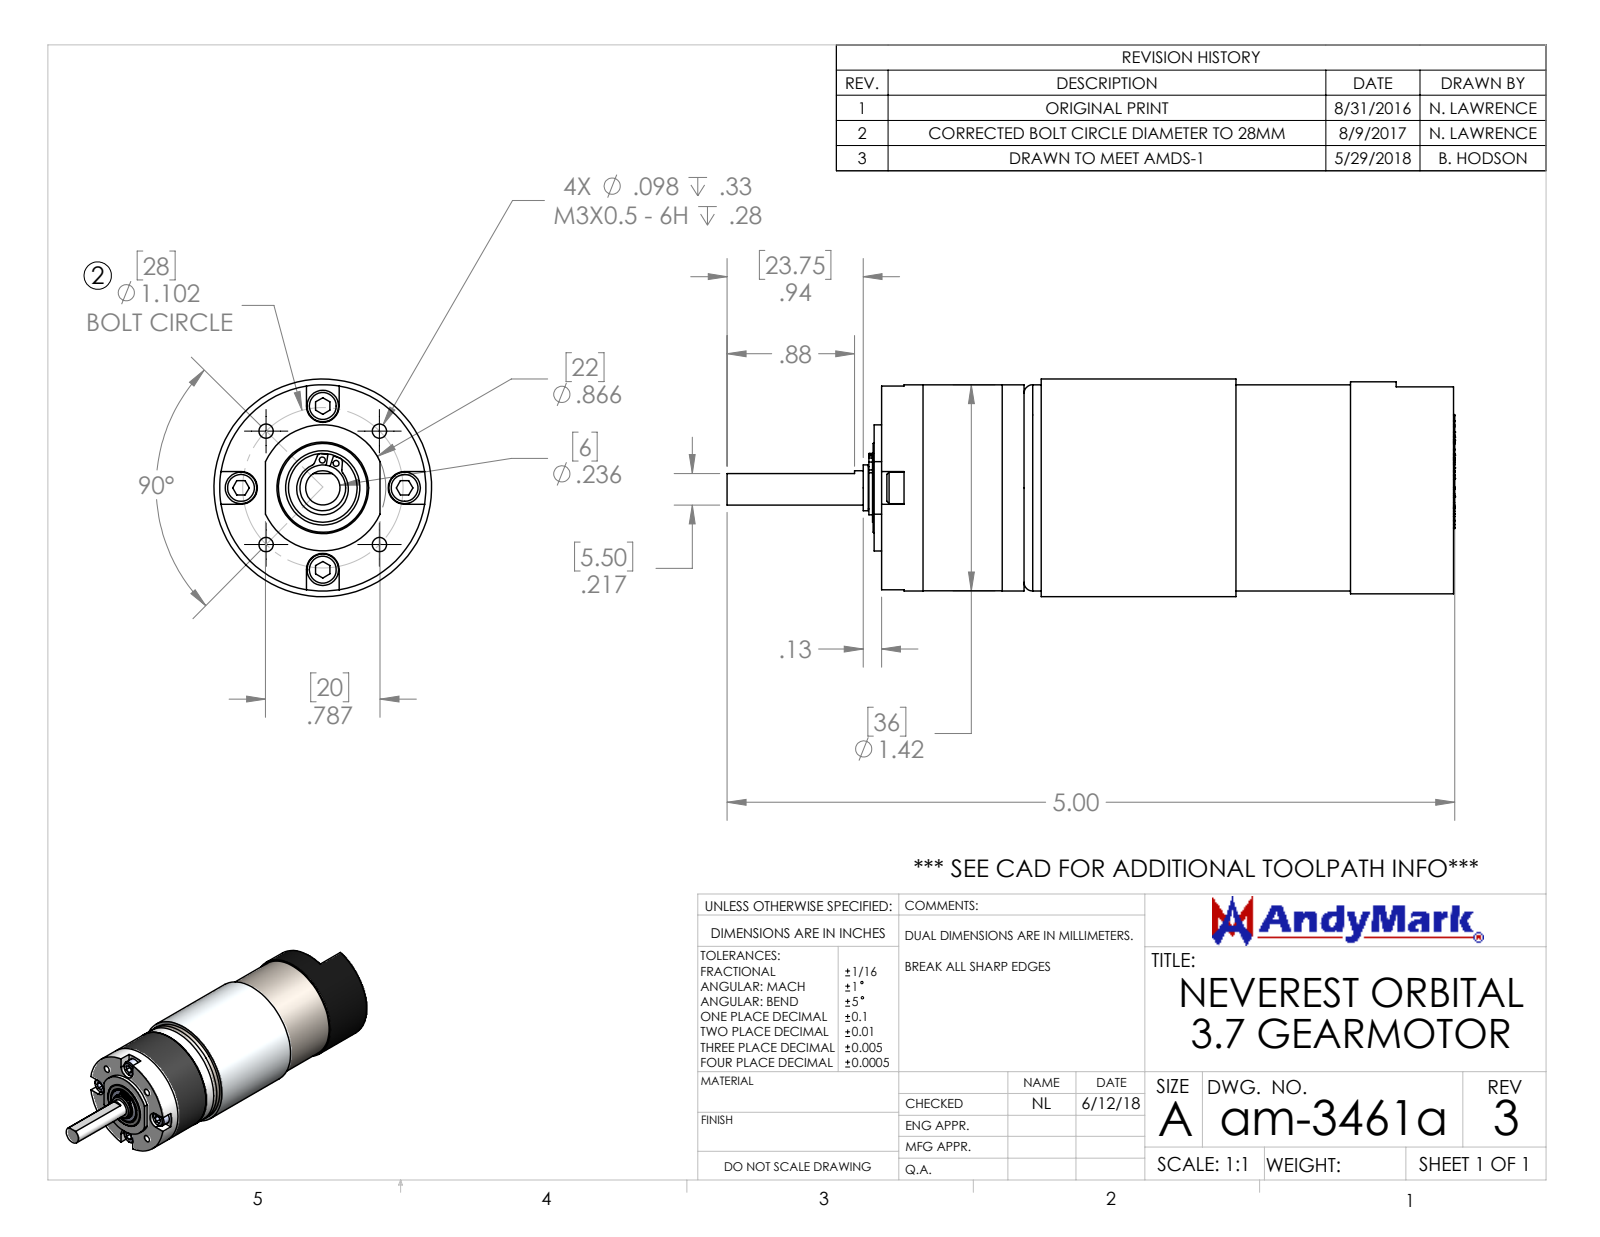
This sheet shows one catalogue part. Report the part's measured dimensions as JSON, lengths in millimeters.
{"part_name": "7804K117_STAINLESS STEEL BALL BEARING_7804K117; NeveRest 4 Gearbox; am-3461a NeveRest Orbital 3.7 Gearmotor; Shim (+4 more)", "step_written_by": "SolidWorks 2021 (AUTOMOTIVE_DESIGN)", "units": "millimeters", "bodies": {"solids": 24, "faces": 599, "planar": 268, "cylindrical": 125, "other": 206}, "overall_size": [127, 38, 38], "volume_mm3": 103700, "surface_area_mm2": 21760, "round_holes": [[2.5, 10], [3.2, 5], [1, 2], [3.2, 1], [7.4, 1], [8, 1], [11, 1], [13, 1], [13, 1], [16, 1]], "round_bosses_or_shafts": [[5.5, 4], [3, 4], [38, 1], [37, 1], [36, 1], [35.9, 1], [12, 1], [6, 1]], "partial_cylinders_radius": [[0.7, 4], [2.8, 3], [2.9, 1], [4.5, 1], [11, 1]], "face_to_face_distances": [75, 99.9, 24.9, 5, 10, 65, 89.9, 101.2, 91.2, 26.2], "hole_center_spacings": [10.8, 26.1, 10.4, 14, 14.3, 18.8, 19.8, 20.2]}
